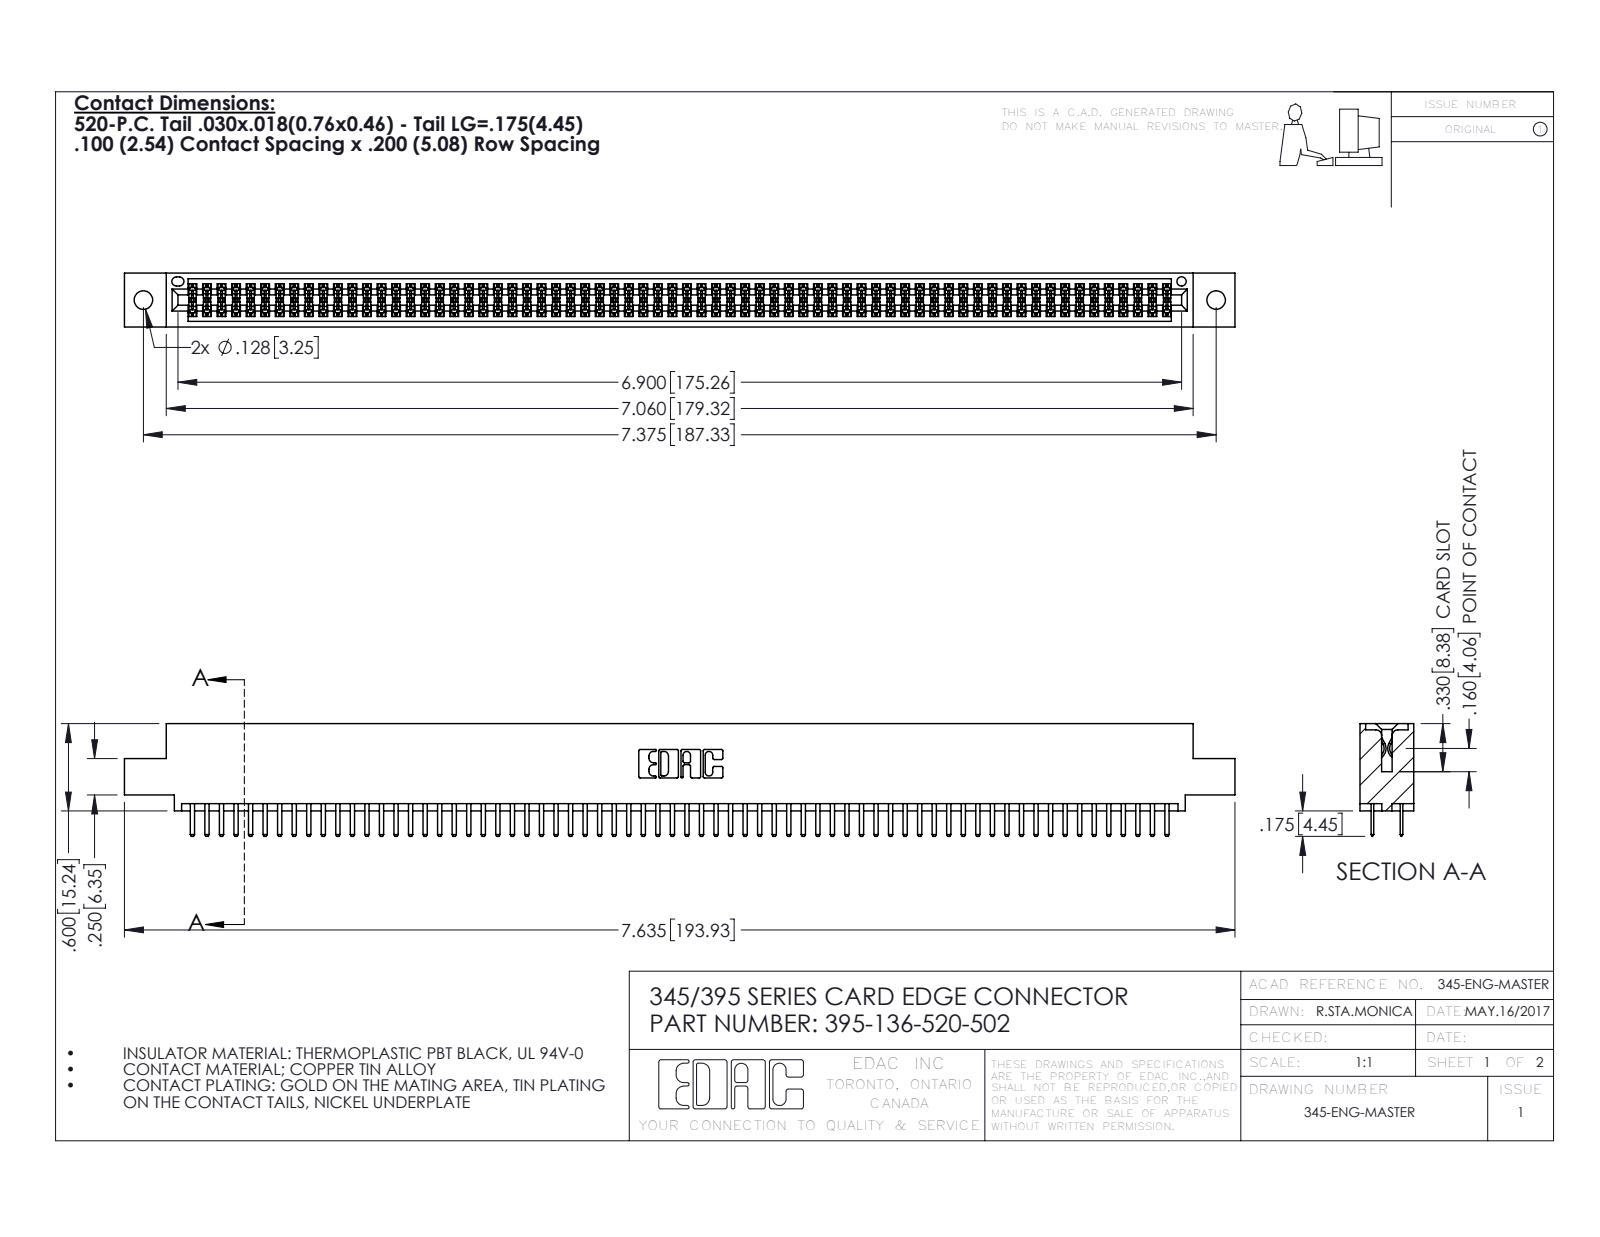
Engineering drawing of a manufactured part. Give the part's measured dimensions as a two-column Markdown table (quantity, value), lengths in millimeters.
| quantity | value |
| --- | --- |
| part name | 345-292-001_345-293-120; 345 Part_0.110 Offset - 0.128 Dia; 395-136-520-502 |
| STEP written by | SolidWorks 2016 (CONFIG_CONTROL_DESIGN) |
| units | millimeters |
| bodies | 137 solids, 7474 faces (4844 planar, 2630 cylindrical, 0 other) |
| overall size | 193.9 × 19.7 × 9.4 |
| volume | 18 910 mm³ |
| surface area | 28 150 mm² |
| round holes (diameter × count) | 3.3 × 2, 1.6 × 1 |
| partial cylindrical surfaces (radius × count) | 0.2 × 204, 0.3 × 140, 0.3 × 22, 0.2 × 6, 0.8 × 6, 0.7 × 3, 0.4 × 2, 0.5 × 2 |
| main face-to-face distances | 1.8, 7.6, 5.1, 9.4, 2.5, 6.9, 0.6, 5.7, 0.6, 1.8 |
| hole center spacings | 6.9, 181.3, 187.3 |
